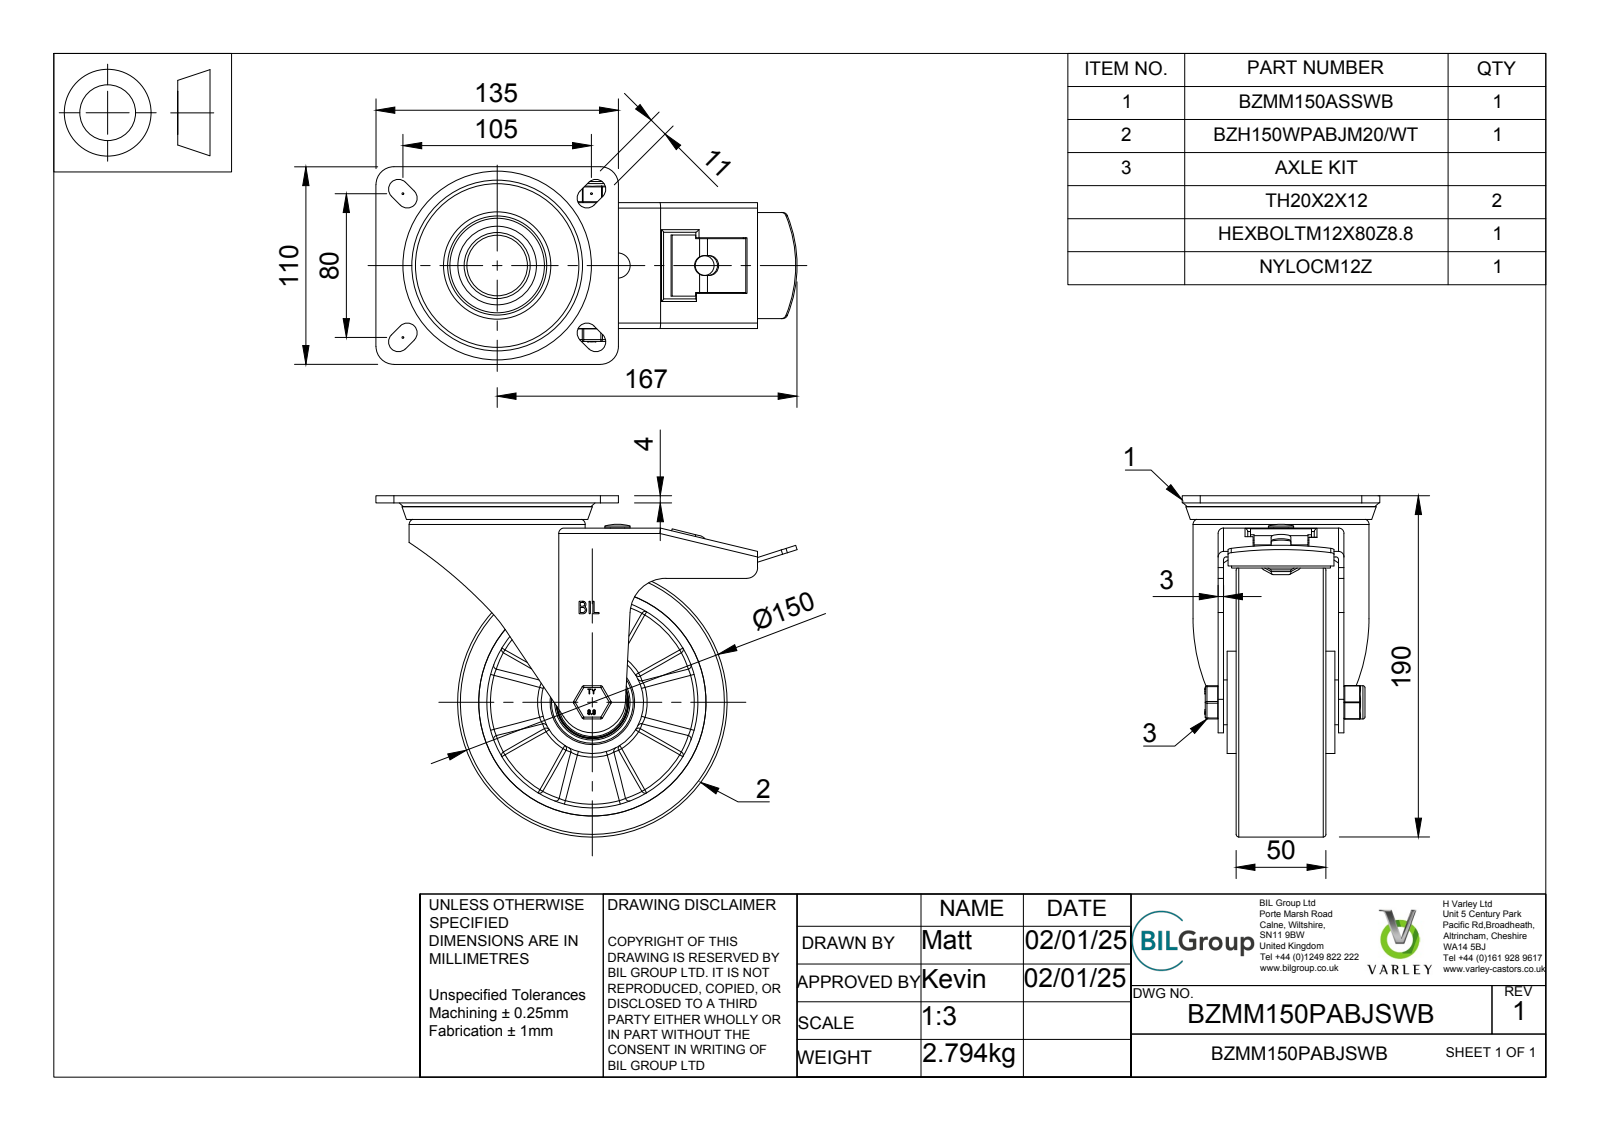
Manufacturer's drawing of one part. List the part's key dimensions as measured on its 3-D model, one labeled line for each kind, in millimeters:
Part name (STEP PRODUCT): BZMM150PABJSWB v3; BZMM150ASSWB - 64 v1; ZINC PLATED, PRESSED STEEL TOP PLATE; ZINC PLATED, PRESSED STEEL TOP PLATE Geometry (+7 more)
STEP written by: Autodesk Translation Framework v13.20.0.188 (AP242_MANAGED_MODEL_BASED_3D_ENGINEERING_MIM_LF)
Units: millimetres
Bodies: 82 solids, 1014 faces (379 planar, 249 cylindrical, 386 other)
Overall size (bounding box): 234.5 × 190 × 110
Volume: 705 844 mm³ · Surface area: 327 382 mm²
Round holes (diameter × count): ⌀8 ×1, ⌀11 ×1, ⌀12 ×1, ⌀12.2 ×1, ⌀14 ×1, ⌀20 ×1, ⌀28.5 ×1, ⌀29.5 ×1, ⌀33.75 ×1, ⌀39.75 ×1, ⌀40.5 ×1, ⌀42 ×1
Round bosses / shafts (diameter × count): ⌀150 ×1, ⌀98 ×1, ⌀78 ×1, ⌀57 ×1, ⌀50 ×1, ⌀41.5 ×1, ⌀30.5 ×1, ⌀27 ×1
Partial cylindrical surfaces — rounded edges, fillets, slot ends (radius × count): R0.5 ×18, R1 ×12, R1.5 ×10, R5.5 ×10, R0.25 ×6, R2.5 ×6, R3 ×6, R10 ×4
Main face-to-face distances: 3, 5, 7, 9, 4, 10, 60, 57, 14, 67
Hole centre spacings: 67
